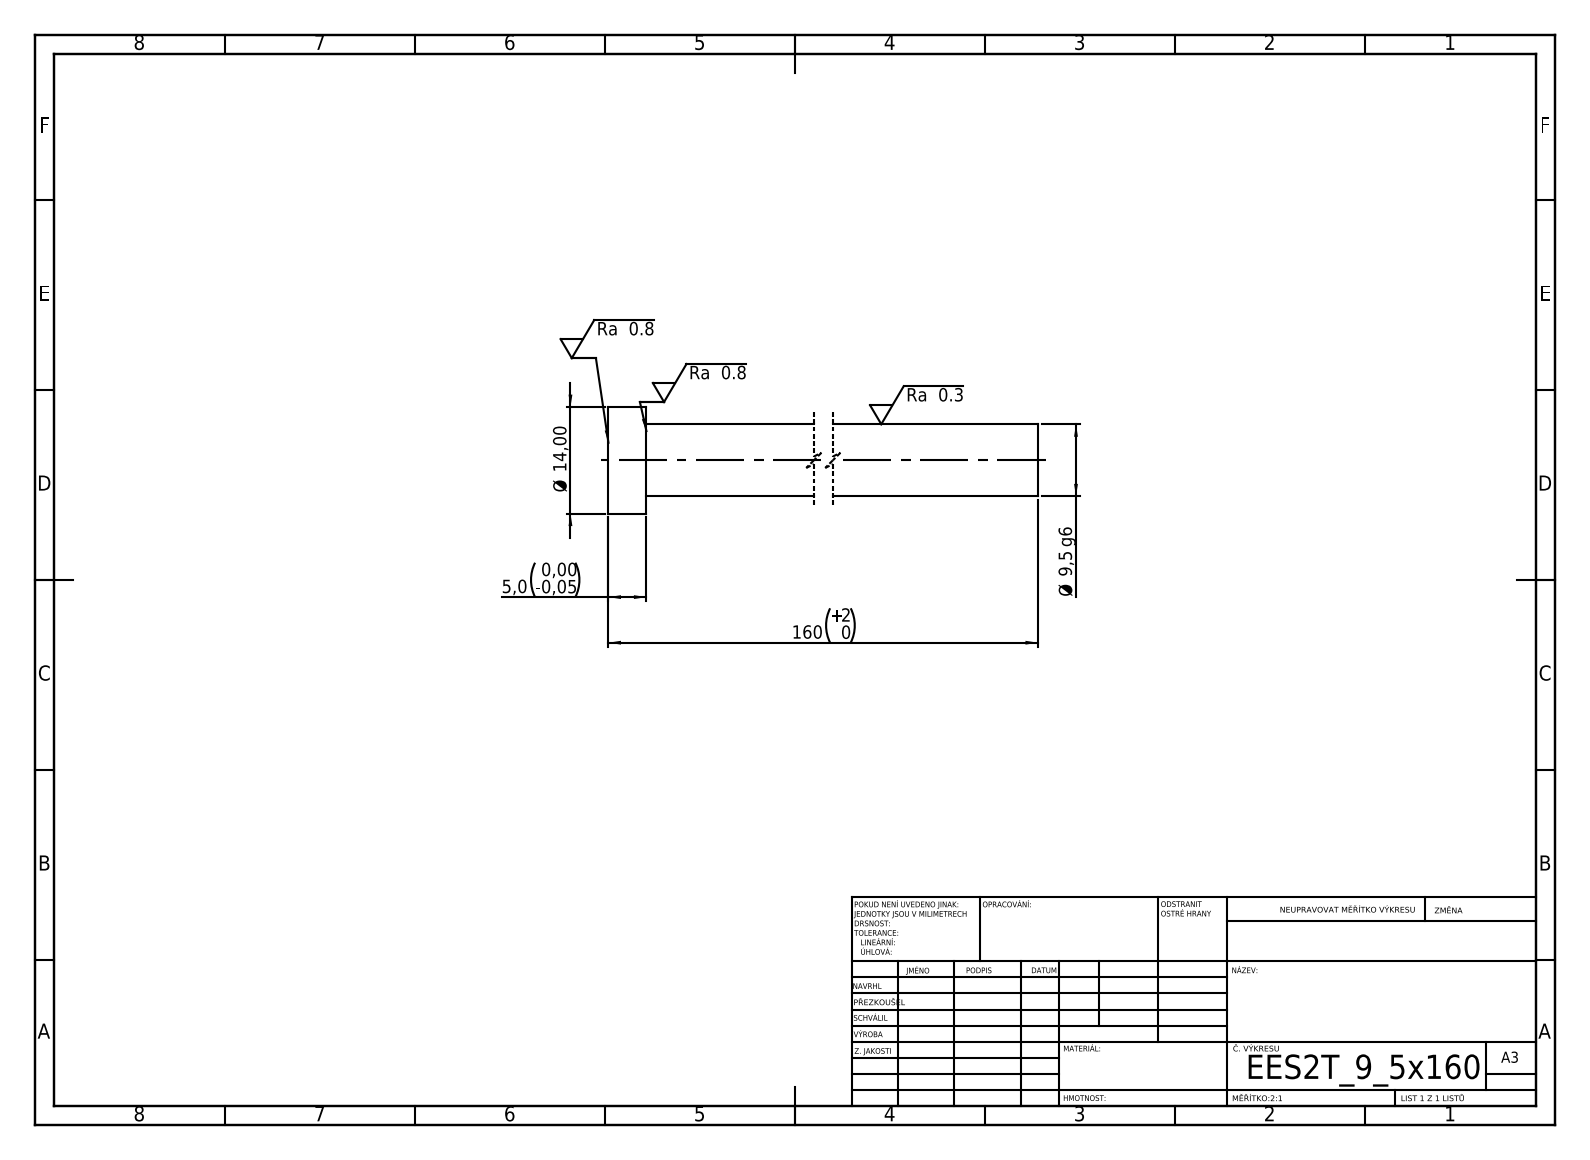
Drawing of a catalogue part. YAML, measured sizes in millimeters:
step_written_by: "SolidWorks 2019 (CONFIG_CONTROL_DESIGN)"
units: millimeters
bodies: {solids: 1, faces: 7, planar: 3, cylindrical: 4, other: 0}
overall_size: [160, 14, 14]
volume: 11756
surface_area: 5154
round_bosses_or_shafts:
  - {diameter: 14, count: 1}
  - {diameter: 9.5, count: 1}
face_to_face_distances: [5, 160, 155]
